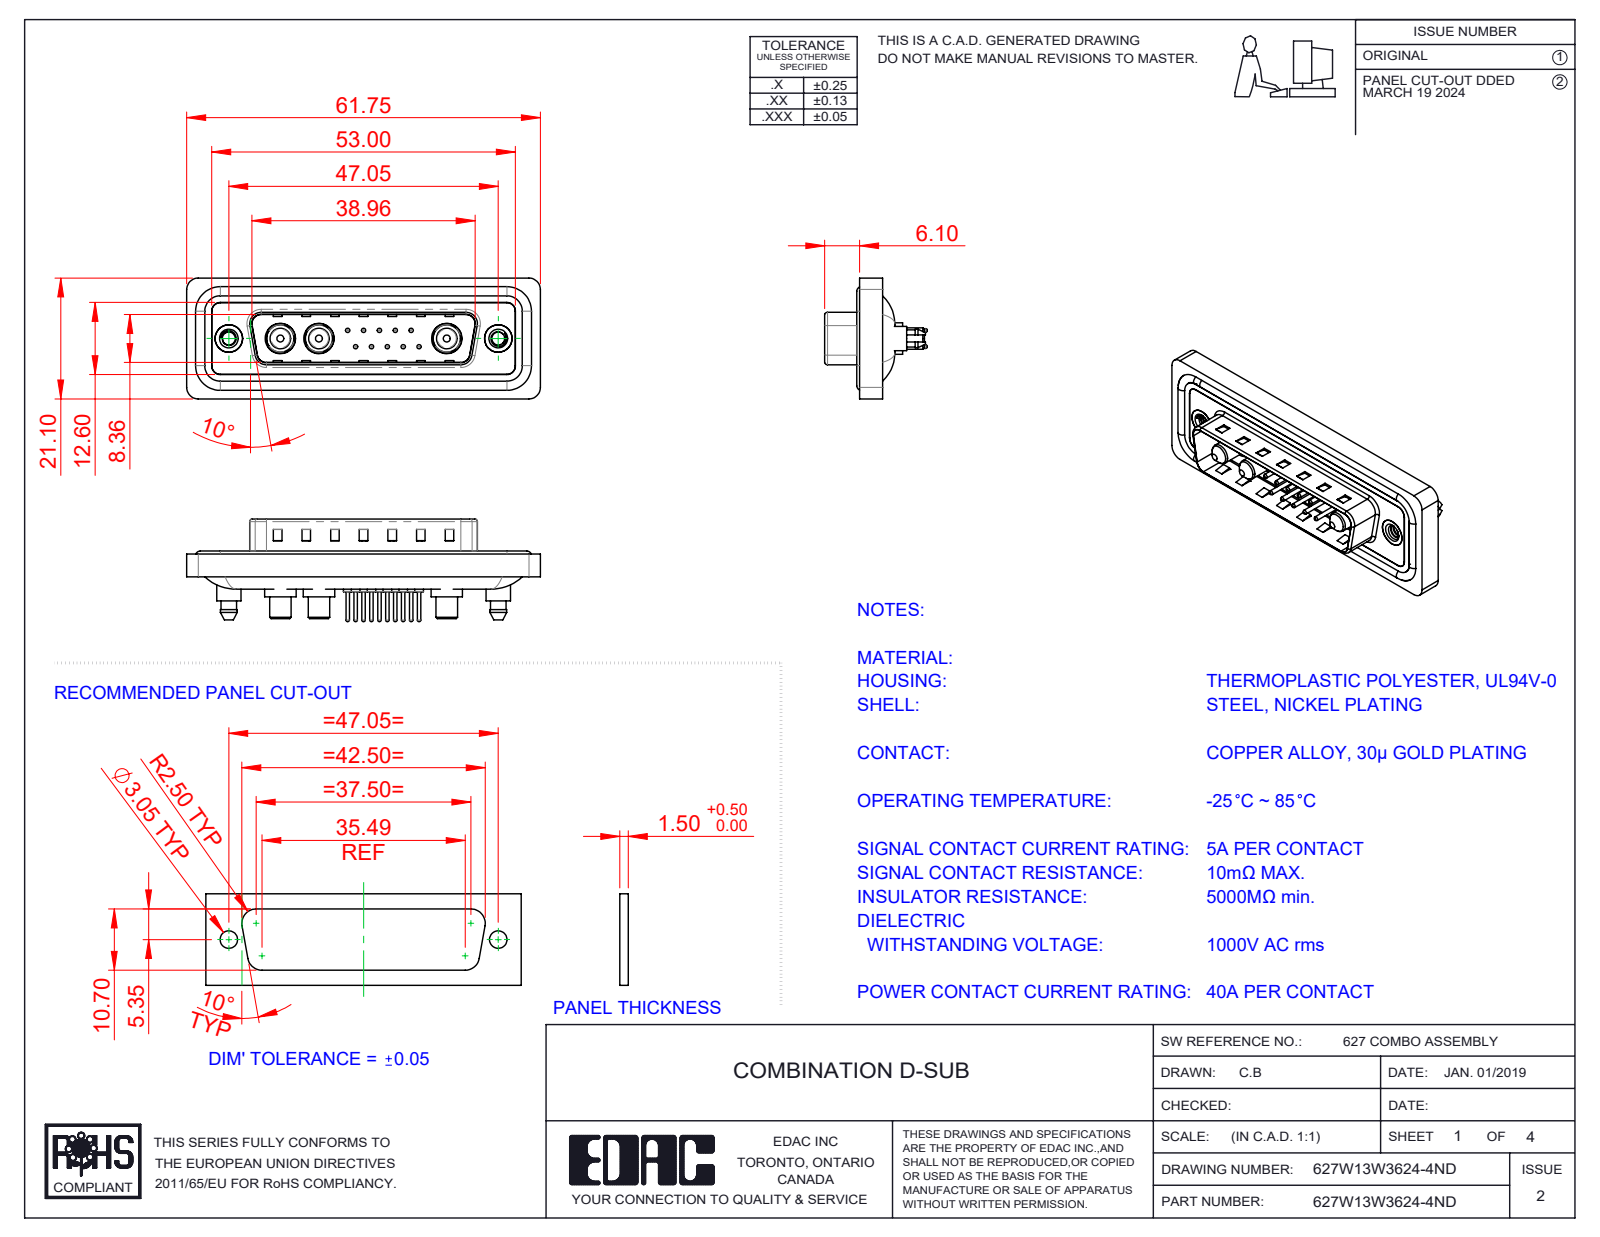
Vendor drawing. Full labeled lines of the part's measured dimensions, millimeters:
Part name (STEP PRODUCT): 627Combo Waterproof Housing_25 Contacts; 627Combo Housing_13W3; 627Combo Contact Row 2_24; Power Pin_40A S (+6 more)
STEP written by: SolidWorks 2023 (CONFIG_CONTROL_DESIGN)
Units: millimetres
Bodies: 23 solids, 1028 faces (325 planar, 425 cylindrical, 278 other)
Overall size (bounding box): 61.75 × 21.1 × 17.9
Volume: 7 525 mm³ · Surface area: 12 244 mm²
Round holes (diameter × count): ⌀0.75 ×10, ⌀1.6 ×10, ⌀2 ×10, ⌀4.85 ×3, ⌀5.3 ×3, ⌀2.26 ×2, ⌀4 ×2, ⌀4.8 ×2, ⌀5 ×2
Round bosses / shafts (diameter × count): ⌀1.5 ×10, ⌀0.6 ×10, ⌀1.6 ×4, ⌀5.5 ×3, ⌀5.2 ×3, ⌀4.75 ×3, ⌀3.75 ×3, ⌀3.6 ×3
Partial cylindrical surfaces — rounded edges, fillets, slot ends (radius × count): R1.5 ×24, R2 ×18, R1.6 ×10, R0.5 ×8, R0.25 ×4, R0.6 ×4, R0.65 ×4, R0.9 ×4
Main face-to-face distances: 0.4, 1.5, 1.1, 1.6, 0.5, 3.1, 2.9, 0.82, 9.58, 4.1
Hole centre spacings: 3.16, 2.77, 5.04, 5.54, 7.49, 5.03, 8.31, 10.11
